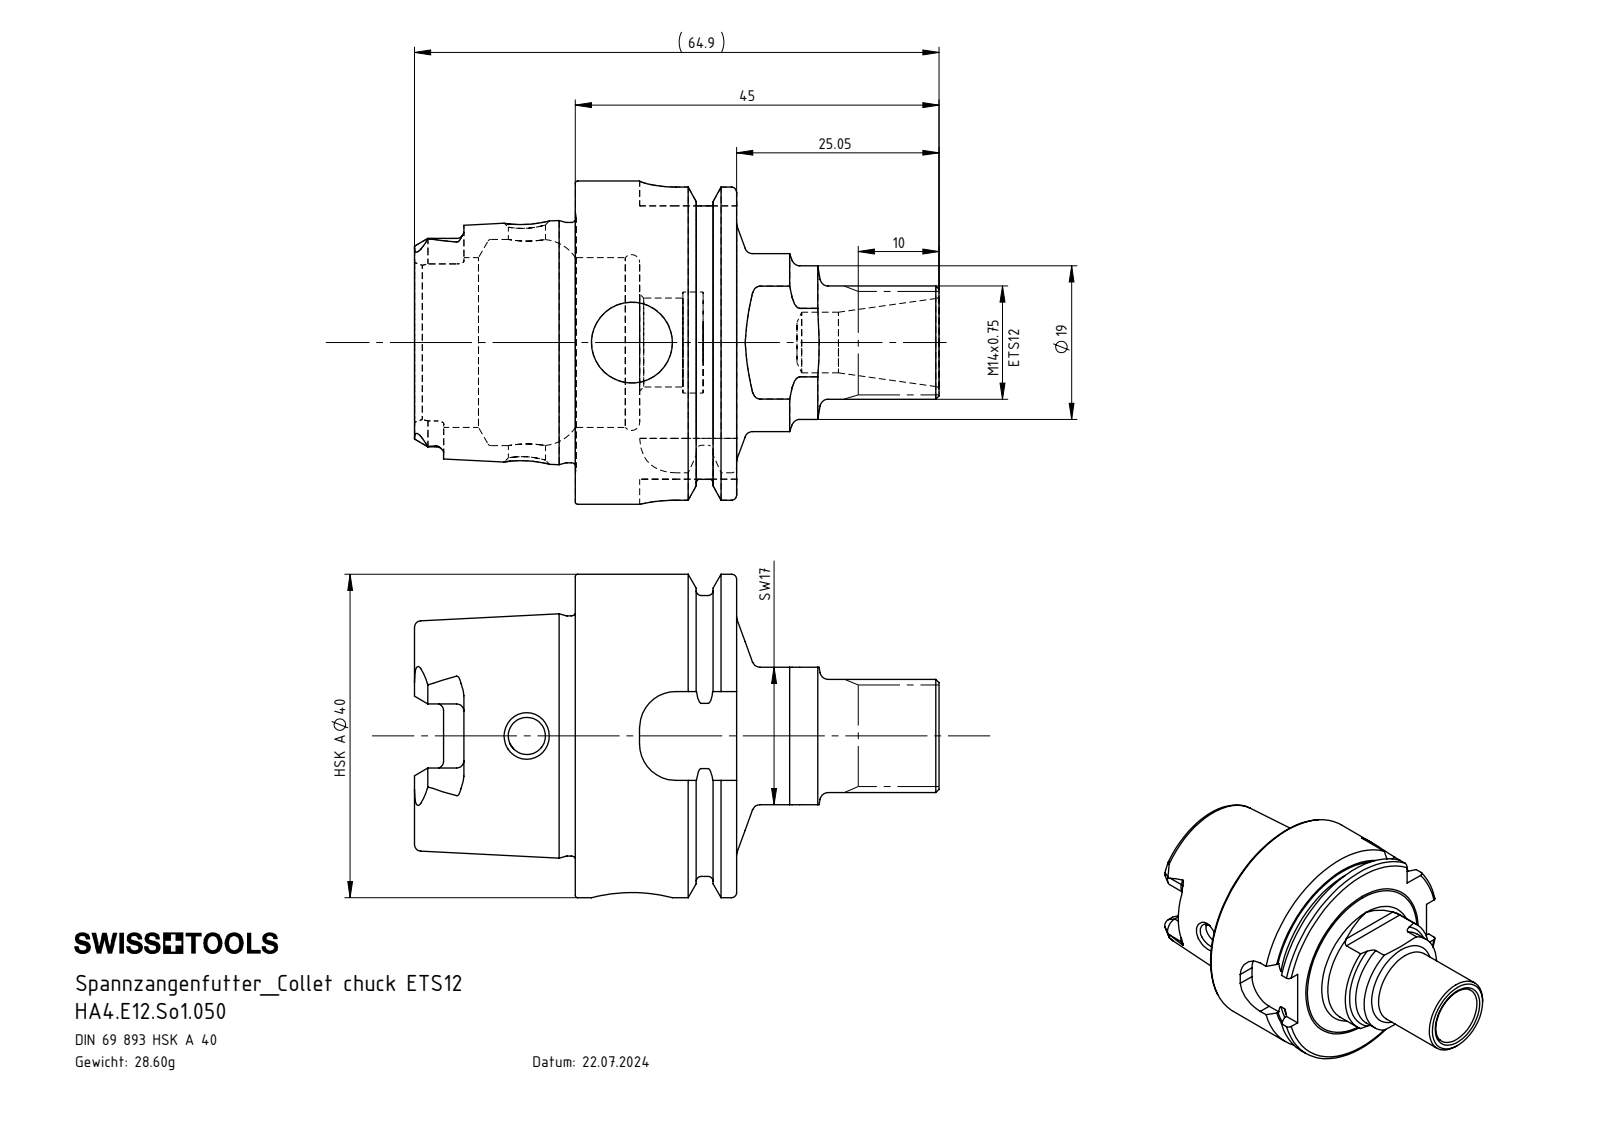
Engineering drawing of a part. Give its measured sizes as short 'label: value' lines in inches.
name: HA4.E12.So1.050; HA4-E12.So1.050_A; E12-ER1.001.012_A
written by: SolidWorks 2022 (AUTOMOTIVE_DESIGN)
unit: in
bodies: 2 solids, 227 faces (56 planar, 68 cylindrical, 103 other)
size: 2.752 × 1.575 × 1.575
volume: 1.857 in³; area: 19.87 in²
holes: 2× ⌀0.394, 1× ⌀0.181, 1× ⌀0.197, 1× ⌀0.295, 1× ⌀0.354, 1× ⌀0.433, 1× ⌀0.492, 1× ⌀0.512, 1× ⌀0.551, 1× ⌀0.827, 1× ⌀1.004
bosses: 1× ⌀1.575, 1× ⌀1.368, 1× ⌀1.17, 1× ⌀0.748
rounds: 6× R0.035, 4× R0.074, 4× R0.177, 2× R0.02, 2× R0.039, 1× R0.433
face distances: 0.785, 0.472, 1.183, 0.313, 1.969, 1.656, 0.669, 0.783, 1.096, 1.569
